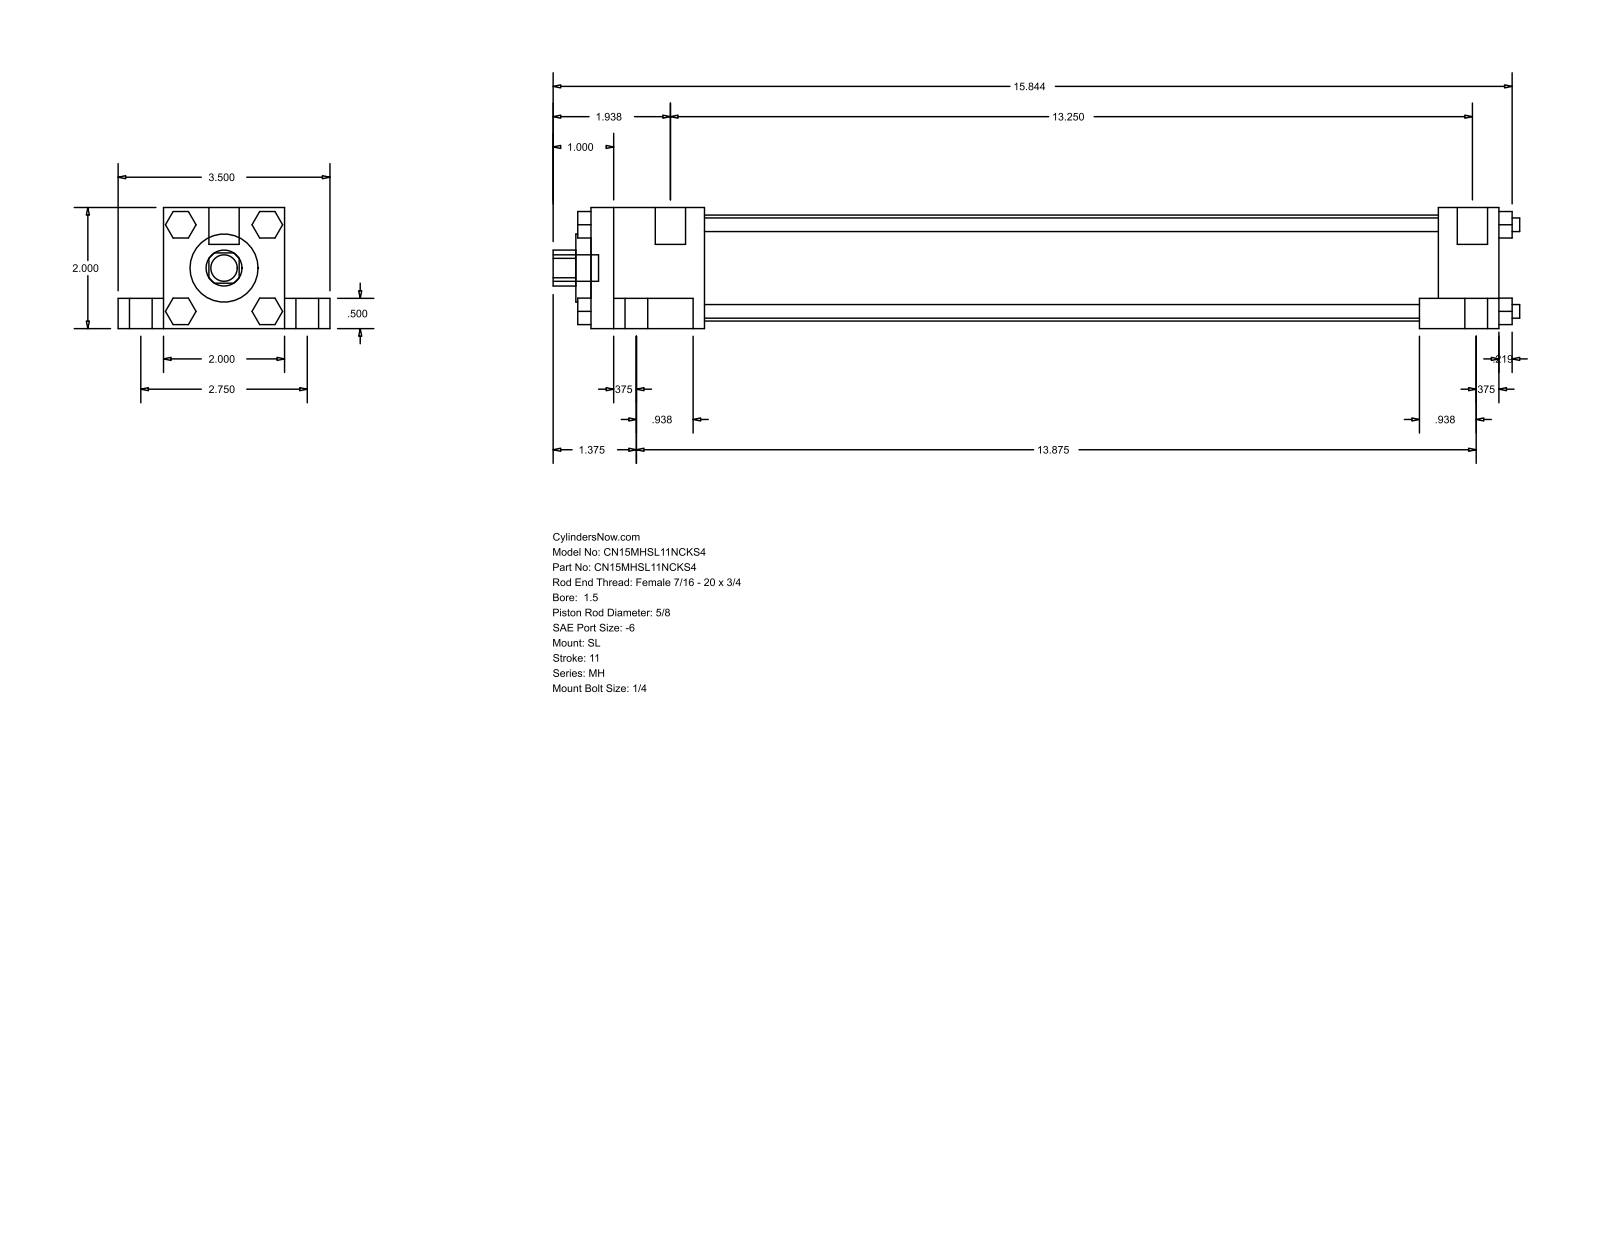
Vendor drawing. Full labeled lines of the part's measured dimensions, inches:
Part name (STEP PRODUCT): MH_SL__0150_0.625
STEP written by: GSSL Pune (CONFIG_CONTROL_DESIGN)
Units: inches
Bodies: 0 solids, 148 faces (112 planar, 36 cylindrical, 0 other)
Overall size (bounding box): 15.969 × 3.5 × 2
Round holes (diameter × count): ⌀0.625 ×1, ⌀1.125 ×1, ⌀1.75 ×1
Round bosses / shafts (diameter × count): ⌀0.625 ×4, ⌀0.375 ×4, ⌀0.225 ×4, ⌀0.219 ×4, ⌀0.5 ×2, ⌀0.437 ×1
Partial cylindrical surfaces — rounded edges, fillets, slot ends (radius × count): R0.297 ×1
Main face-to-face distances: 2, 1.5, 0.75, 0.5, 2.75, 15, 0.375, 1, 1.313, 13.313
